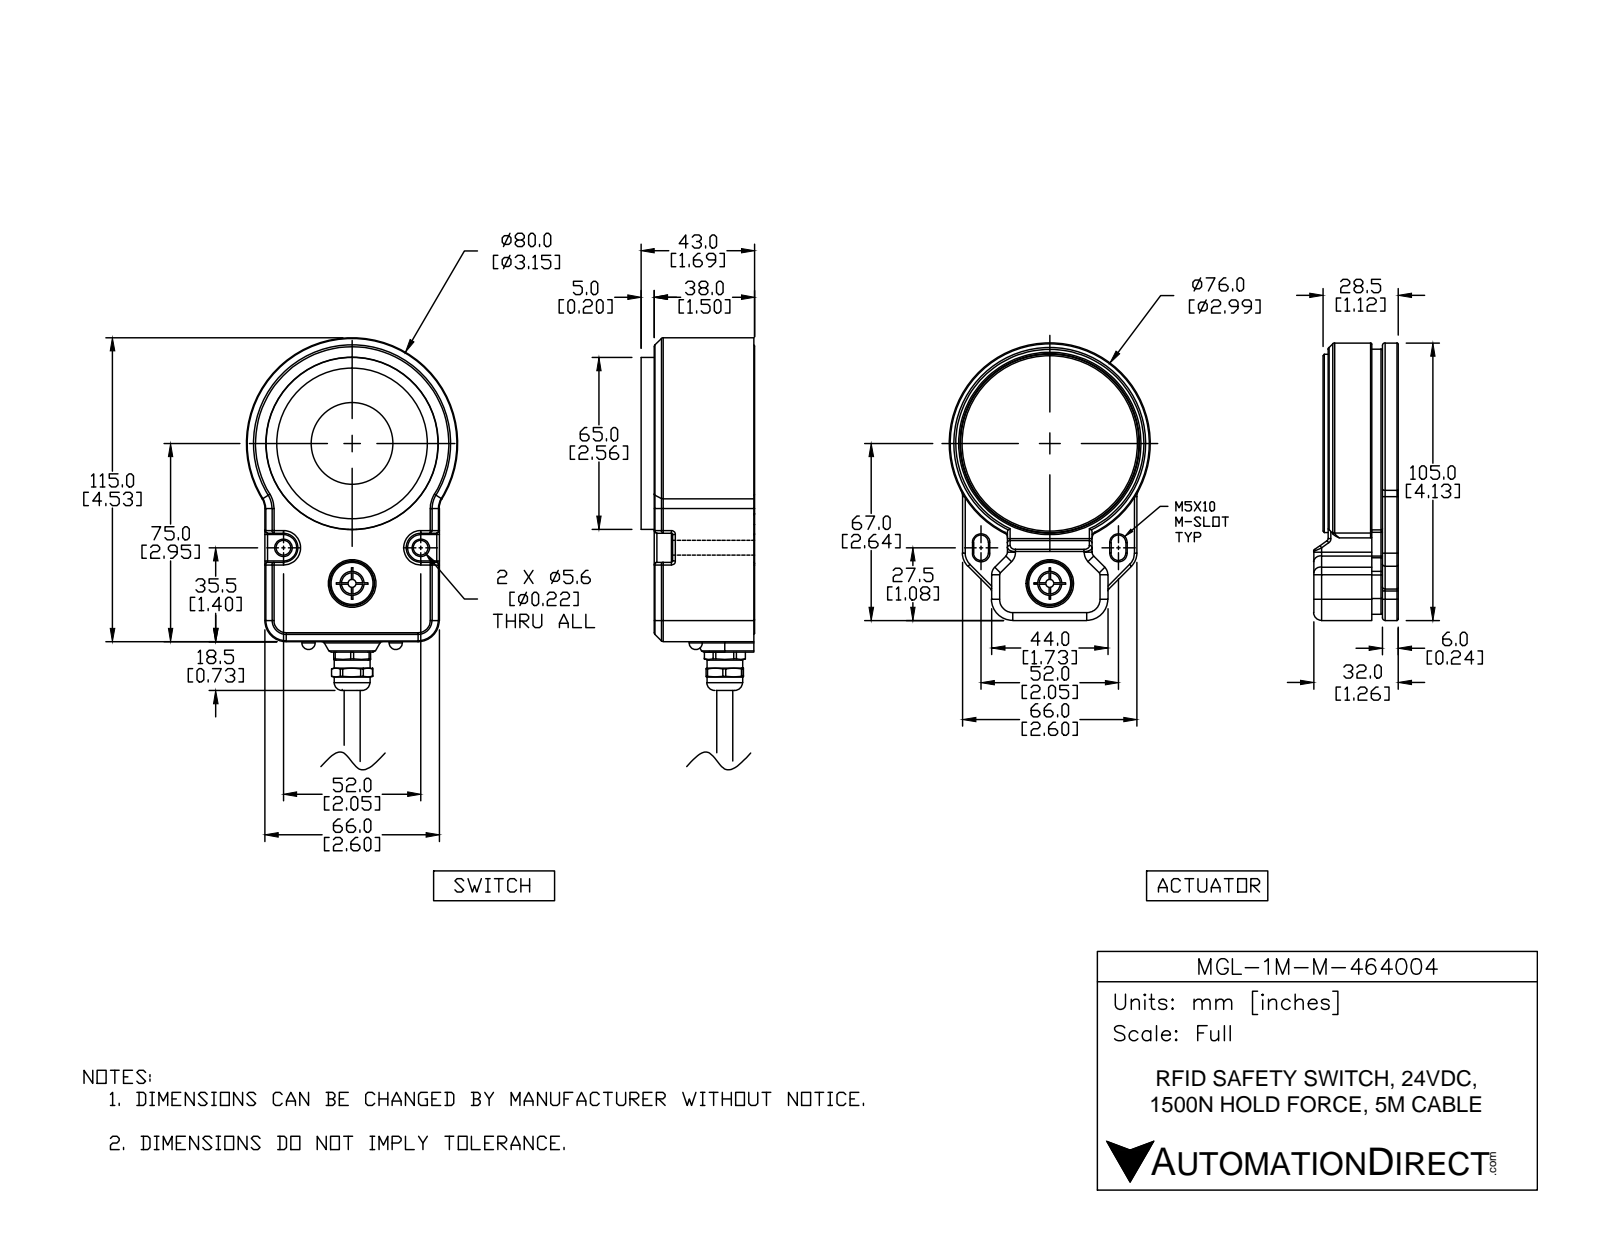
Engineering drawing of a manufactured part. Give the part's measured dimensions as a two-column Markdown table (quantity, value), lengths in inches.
| quantity | value |
| --- | --- |
| part name | MGL-1M-M-464004; MGL-1M-M-464004_1; MGL-1M-M-464004_2 |
| STEP written by | SolidWorks 2017 (AUTOMOTIVE_DESIGN) |
| units | inches |
| bodies | 19 solids, 1753 faces (428 planar, 743 cylindrical, 582 other) |
| overall size | 8.163 × 3.15 × 2.85 |
| volume | 19.31 in³ |
| surface area | 219.5 in² |
| round holes (diameter × count) | 0.098 × 8, 0.13 × 6, 0.197 × 6, 0.453 × 5, 0.157 × 3, 0.315 × 3, 0.354 × 3, 0.22 × 2, 0.276 × 2, 0.374 × 2, 0.465 × 2, 0.252 × 1 |
| round bosses / shafts (diameter × count) | 0.02 × 4, 0.079 × 3, 0.472 × 2, 0.228 × 2, 0.213 × 2, 0.047 × 2, 2.992 × 1, 2.811 × 1 |
| partial cylindrical surfaces (radius × count) | 0.02 × 186, 0.039 × 86, 0.079 × 26, 0.012 × 17, 0.118 × 13, 0.157 × 9, 0.217 × 8, 0.024 × 7 |
| main face-to-face distances | 0.315, 0.236, 2.299, 1.378, 0.118, 2.614, 0.413, 2.201, 2.85, 0.65 |
| hole center spacings | 1.392, 1.969, 0.984, 1.28, 1.537, 0.787, 1.364, 0.349 |
